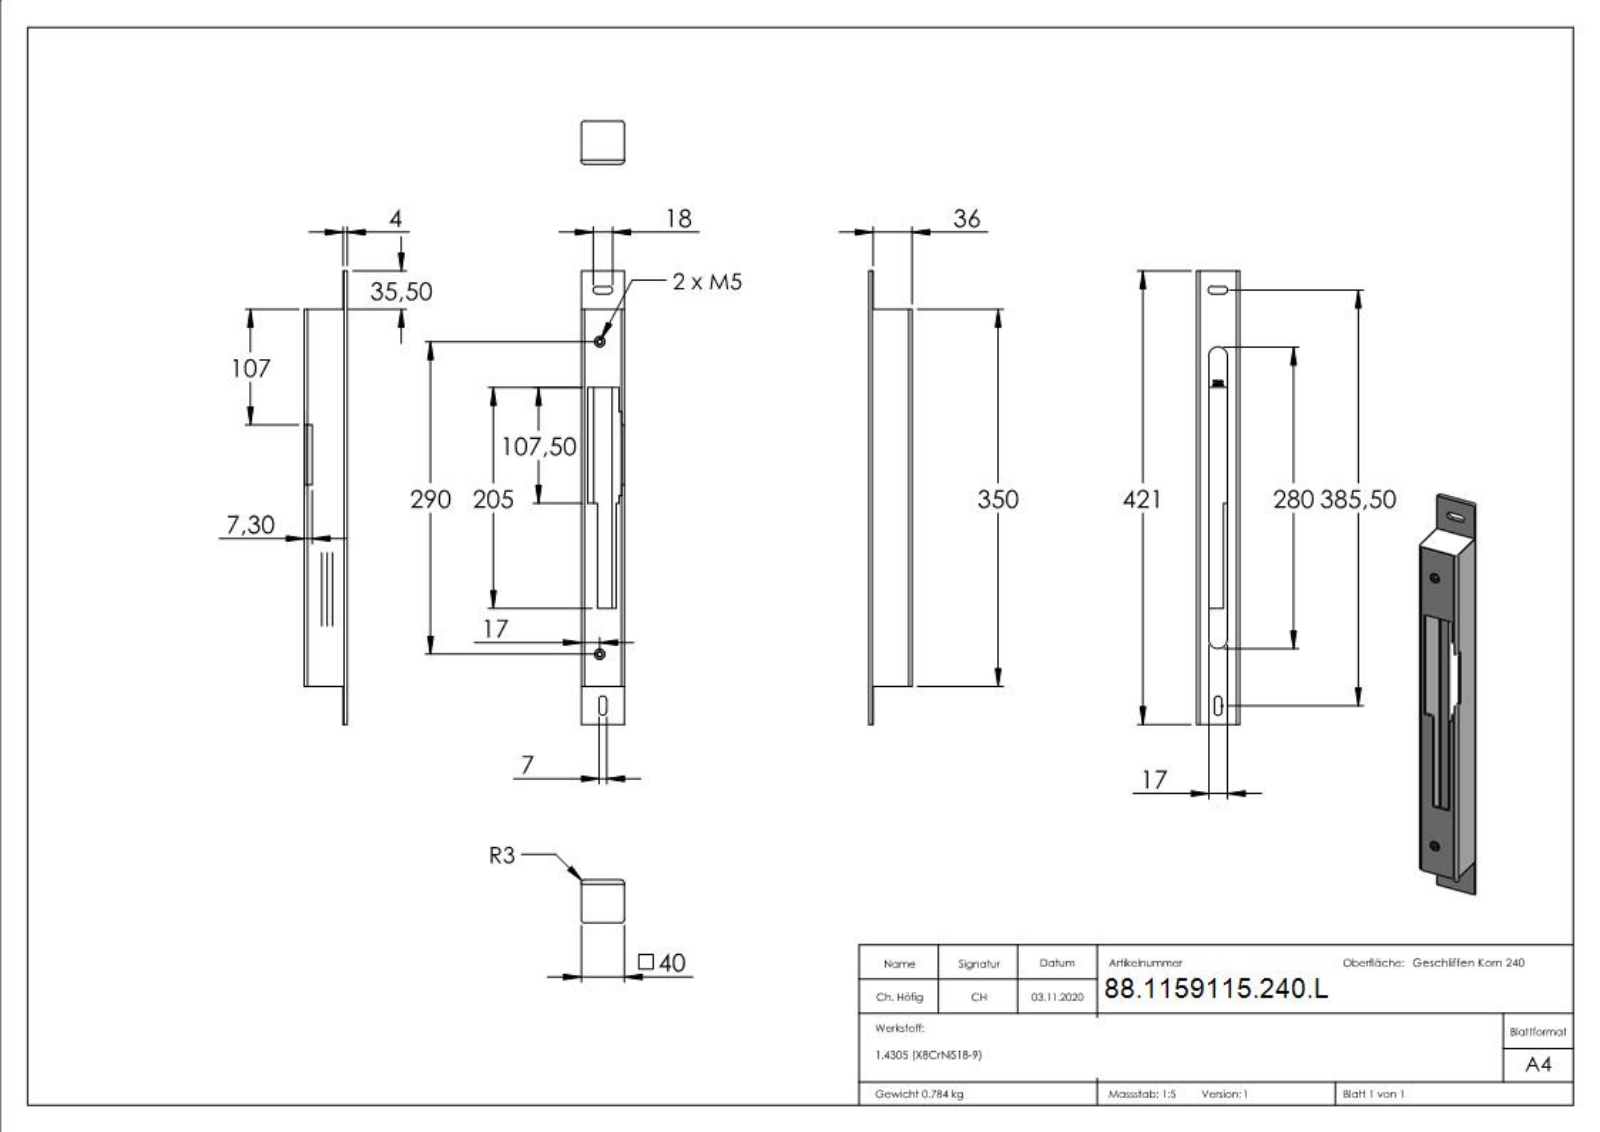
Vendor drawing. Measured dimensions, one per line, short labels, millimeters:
name: 59115-240-L
written by: SolidWorks 2018 (CONFIG_CONTROL_DESIGN)
unit: mm
bodies: 1 solid, 310 faces (185 planar, 37 cylindrical, 88 other)
size: 421 × 40 × 40
volume: 99 241 mm³; area: 97 542 mm²
holes: 2× ⌀4.2, 2× ⌀5.5, 2× ⌀9.55
bosses: 2× ⌀9.35, 2× ⌀6.5
rounds: 4× R1, 4× R3, 4× R3.5, 2× R8.5
face distances: 2, 38, 36, 40, 4, 34, 348, 350, 346, 26.5
hole spacings: 290
